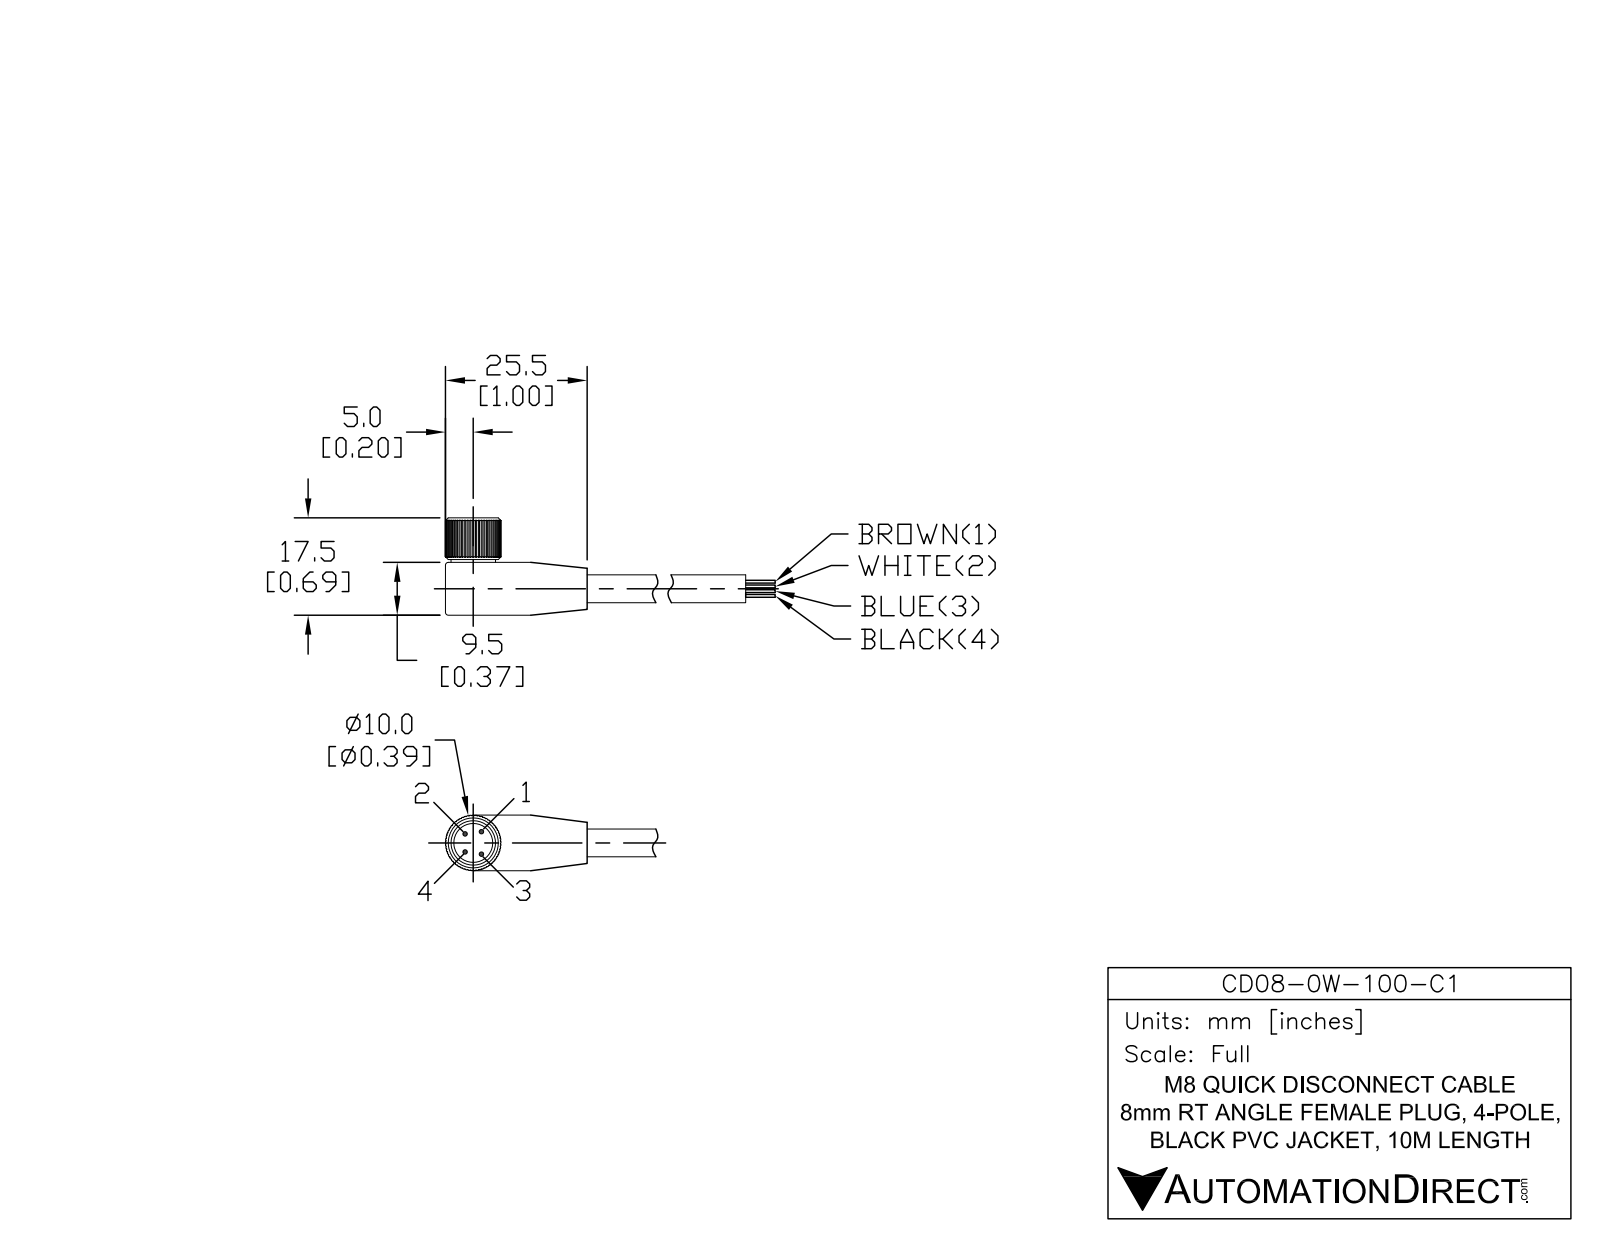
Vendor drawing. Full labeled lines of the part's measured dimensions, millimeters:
Part name (STEP PRODUCT): CD08-0W-100-C1
STEP written by: SolidWorks 2017 (AUTOMOTIVE_DESIGN)
Units: millimetres
Bodies: 4 solids, 306 faces (220 planar, 83 cylindrical, 3 other)
Overall size (bounding box): 128.6 × 19.1 × 10
Volume: 4 341 mm³ · Surface area: 3 353 mm²
Round holes (diameter × count): ⌀0.9 ×4, ⌀7.2 ×1, ⌀8 ×1
Round bosses / shafts (diameter × count): ⌀10 ×2, ⌀7 ×1, ⌀6.6 ×1, ⌀4.8 ×1
Partial cylindrical surfaces — rounded edges, fillets, slot ends (radius × count): R4.9 ×1
Main face-to-face distances: 7.7, 0.6, 9, 7.1, 100, 4.6, 3.1, 4, 2.5, 5.2
Hole centre spacings: 2.19, 2.5, 3.03, 4.69, 3.2, 4
